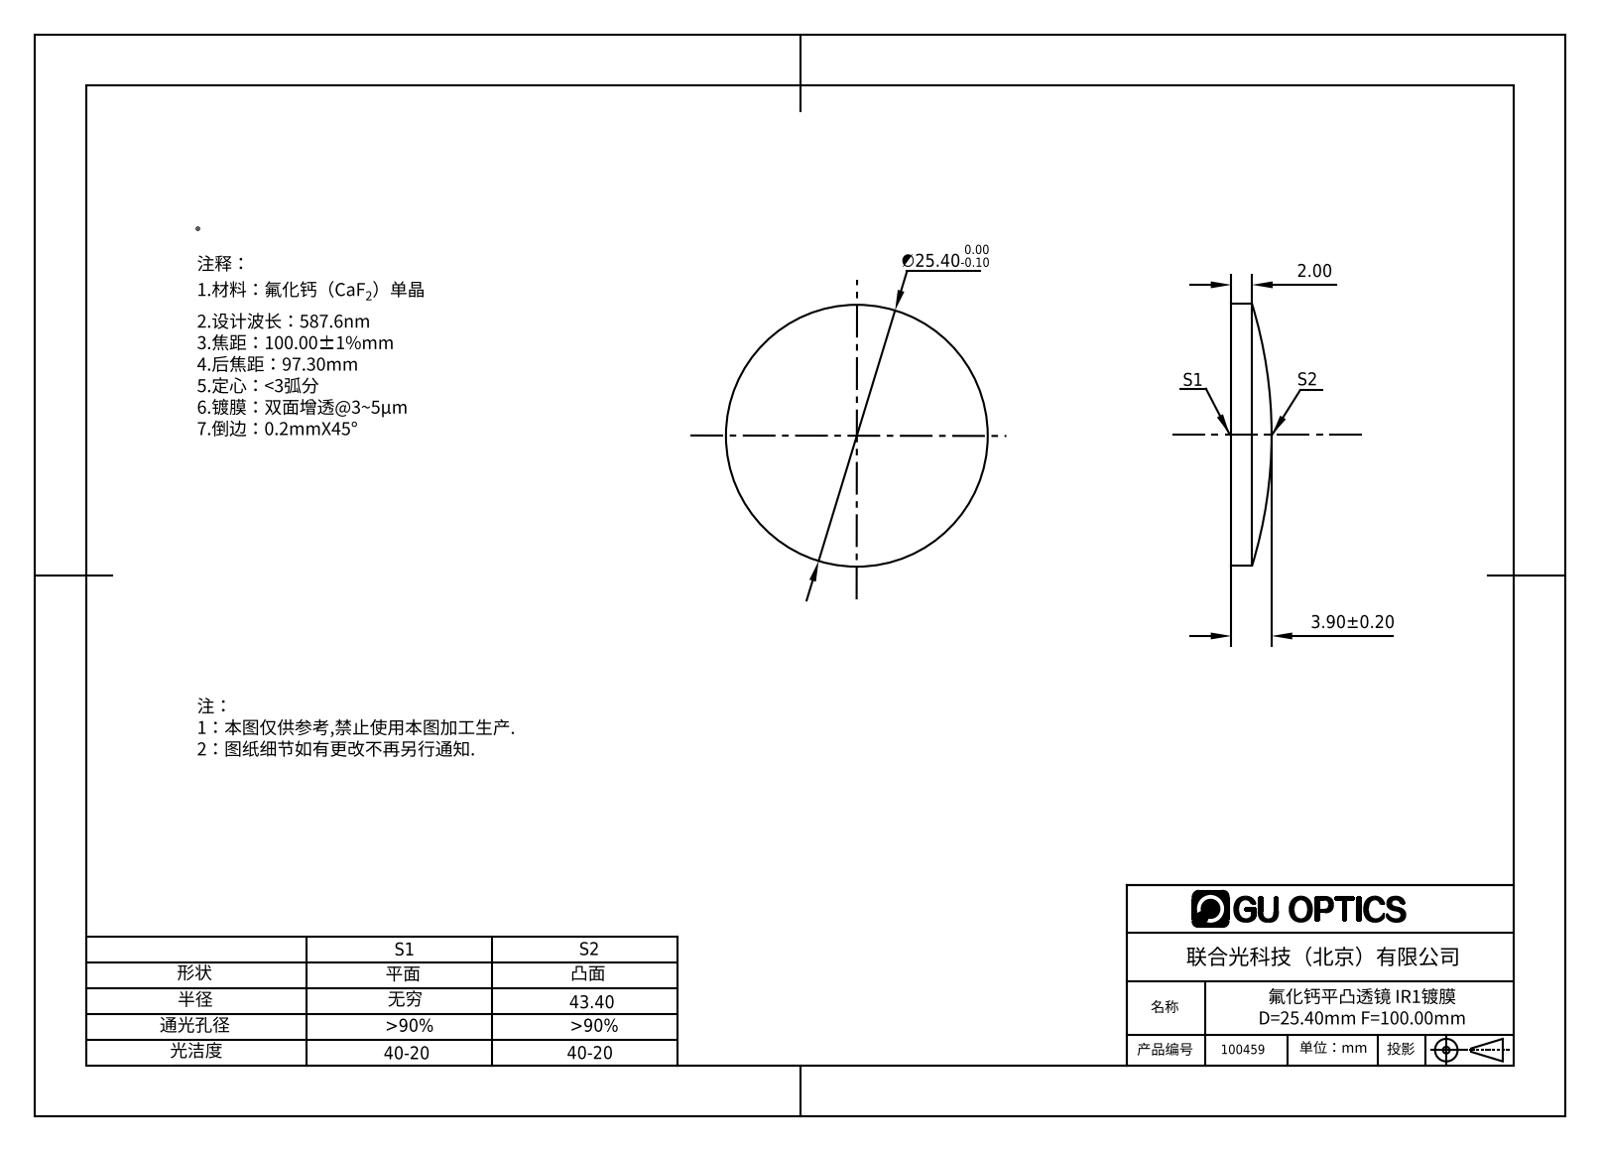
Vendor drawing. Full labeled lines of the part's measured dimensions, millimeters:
Part name (STEP PRODUCT): 100449
STEP written by: SolidWorks 2016 (AUTOMOTIVE_DESIGN)
Units: millimetres
Bodies: 1 solid, 5 faces (1 planar, 2 cylindrical, 2 other)
Overall size (bounding box): 25.4 × 25.4 × 3.9
Volume: 1 498 mm³ · Surface area: 1 184 mm²
Round bosses / shafts (diameter × count): ⌀25.4 ×1
